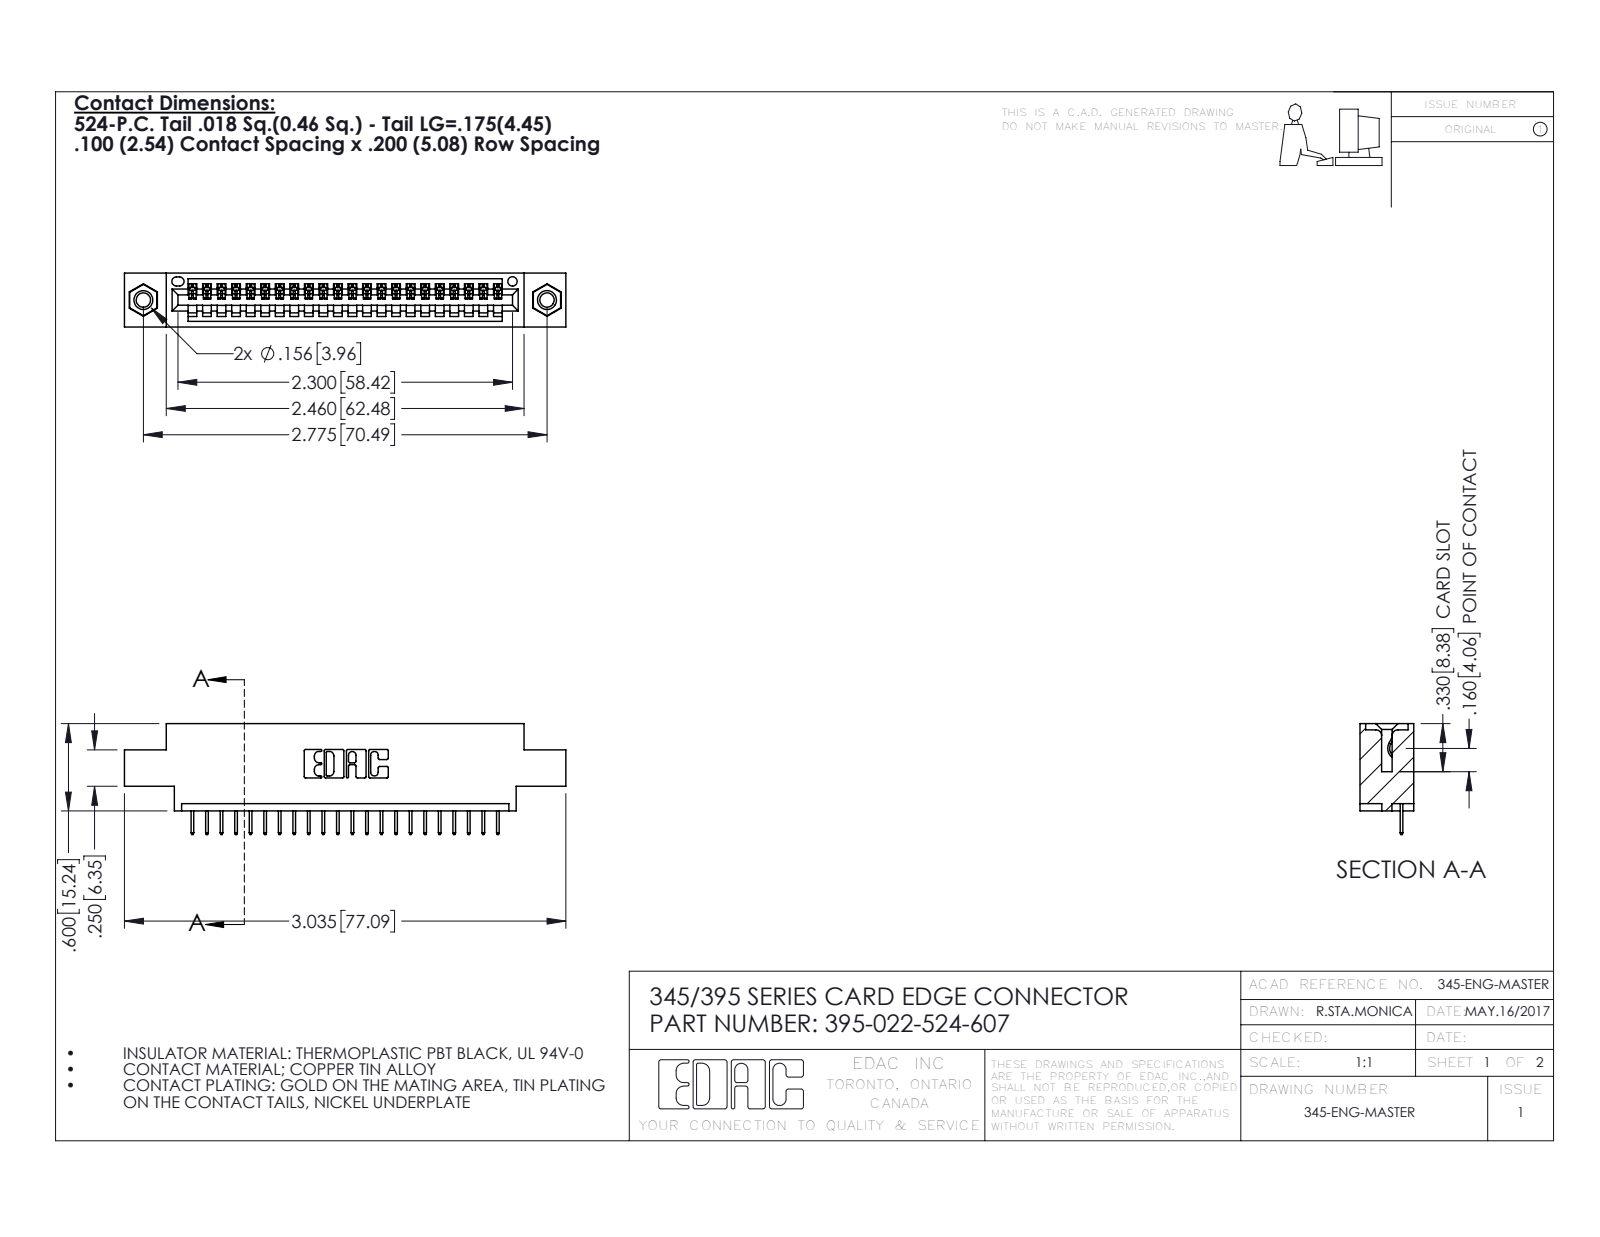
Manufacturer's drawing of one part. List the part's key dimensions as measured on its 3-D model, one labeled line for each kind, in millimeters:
Part name (STEP PRODUCT): 395-022-524-607; 345-292-001_345-293-124; 345 Part_0.170 Offset - 0.156 Dia-TI; 345-250-001_345-250-005-103
STEP written by: SolidWorks 2016 (CONFIG_CONTROL_DESIGN)
Units: millimetres
Bodies: 25 solids, 1554 faces (1128 planar, 410 cylindrical, 16 other)
Overall size (bounding box): 77.1 × 19.4 × 9.4
Volume: 6 950 mm³ · Surface area: 8 839 mm²
Round holes (diameter × count): ⌀2.5 ×2, ⌀3.2 ×2, ⌀4 ×2, ⌀1.6 ×1
Round bosses / shafts (diameter × count): ⌀3.9 ×2
Partial cylindrical surfaces — rounded edges, fillets, slot ends (radius × count): R0.2 ×44, R0.3 ×22, R0.2 ×6, R0.8 ×6, R0.7 ×3, R0.8 ×2, R1 ×2, R0.4 ×1
Main face-to-face distances: 1.8, 7.6, 9.4, 5.1, 2.5, 6.9, 0.6, 5.7, 1.8, 4.4
Hole centre spacings: 6.9, 64.5, 70.5
